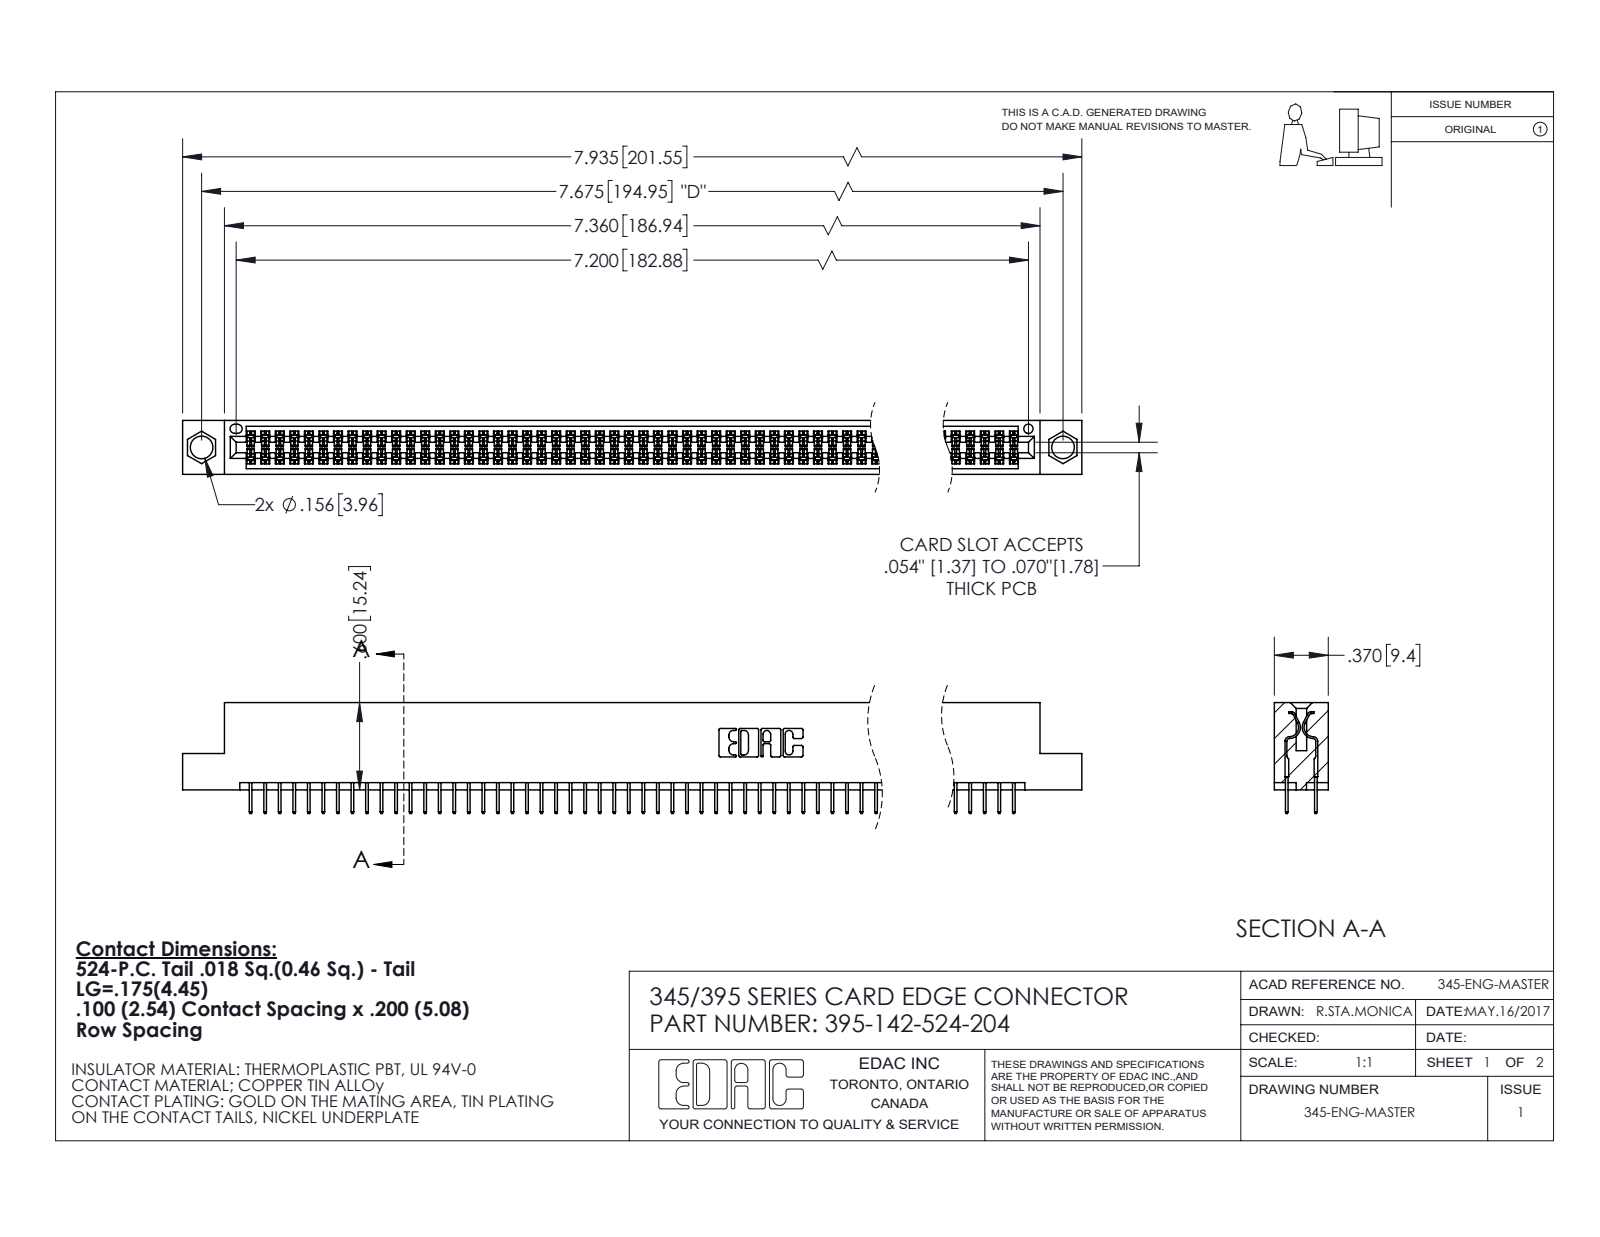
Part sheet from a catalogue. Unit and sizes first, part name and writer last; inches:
Units: inches
Overall size (bounding box): 7.935 × 0.762 × 0.37
Round holes (diameter × count): ⌀0.156 ×2, ⌀0.064 ×1
Partial cylindrical surfaces — rounded edges, fillets, slot ends (radius × count): R0.006 ×213, R0.01 ×22, R0.007 ×6, R0.031 ×6, R0.026 ×3, R0.014 ×2, R0.019 ×2, R0.022 ×2
Main face-to-face distances: 0.072, 0.298, 0.2, 0.37, 0.098, 0.272, 0.025, 0.225, 0.072, 0.175
Hole centre spacings: 0.27, 7.439, 7.675
Volume: 1.192 in³ · Surface area: 44.5 in²
Bodies: 143 solids, 7808 faces (5632 planar, 2176 cylindrical, 0 other)
Part name (STEP PRODUCT): 345 Part_Flush Mounting Lugs - 0.156 Dia-TI; 395-142-524-204; 345-292-001_345-293-124
STEP written by: SolidWorks 2020 (CONFIG_CONTROL_DESIGN)
